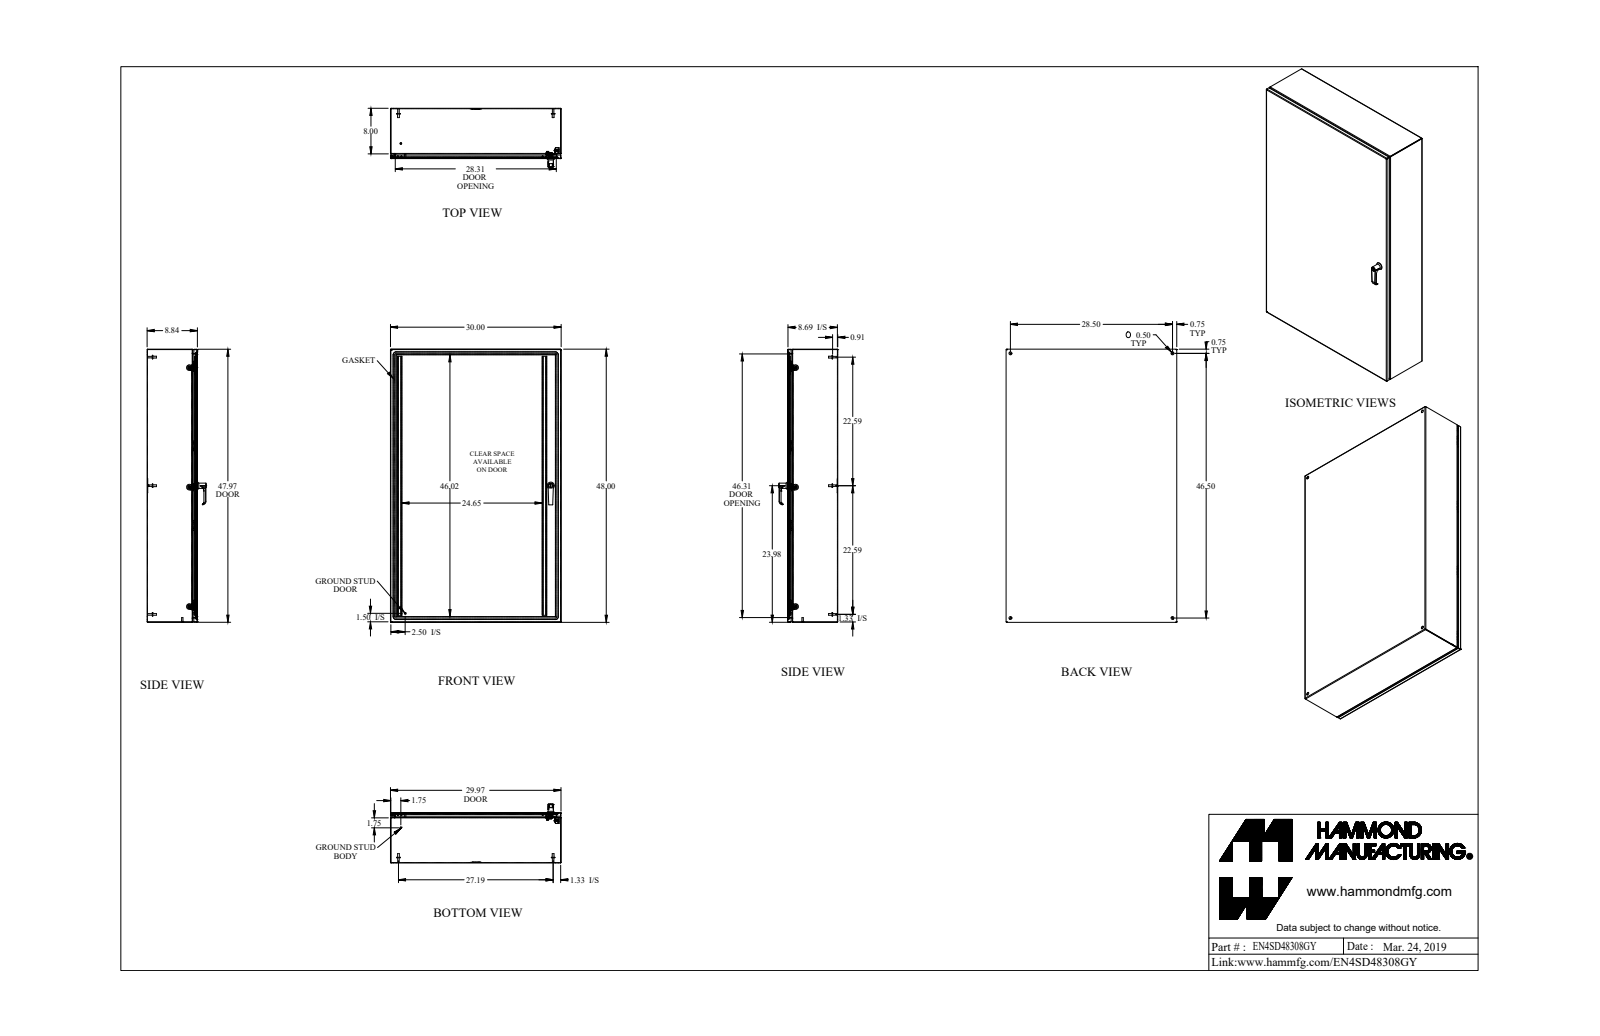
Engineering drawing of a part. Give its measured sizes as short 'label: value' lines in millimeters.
name: EN4SD48308GY_Default
written by: SolidWorks 2019 (CONFIG_CONTROL_DESIGN)
unit: mm
bodies: 53 solids, 1457 faces (632 planar, 538 cylindrical, 287 other)
size: 1219.2 × 762 × 263.3
volume: 5 735 000 mm³; area: 6 266 000 mm²
holes: 6× ⌀4.5, 4× ⌀12.7, 3× ⌀5, 3× ⌀6.4, 3× ⌀6.7, 3× ⌀10.5, 2× ⌀6.5, 2× ⌀8, 2× ⌀10, 1× ⌀4.4, 1× ⌀6.1, 1× ⌀6.1
bosses: 7× ⌀6.4, 6× ⌀15.9, 6× ⌀9.5, 6× ⌀8, 6× ⌀6.9, 6× ⌀4, 3× ⌀25.4, 2× ⌀16
rounds: 20× R0.9, 20× R2.7, 15× R0.8, 12× R1.1, 12× R2.1, 8× R0.2, 8× R1, 8× R1.6
face distances: 1.8, 222.6, 220.8, 224.5, 760.2, 1217.4, 758.3, 762, 1215.5, 1219.2
hole spacings: 20, 63.7, 532.9, 533.1, 533.4, 699, 723.9, 1066
